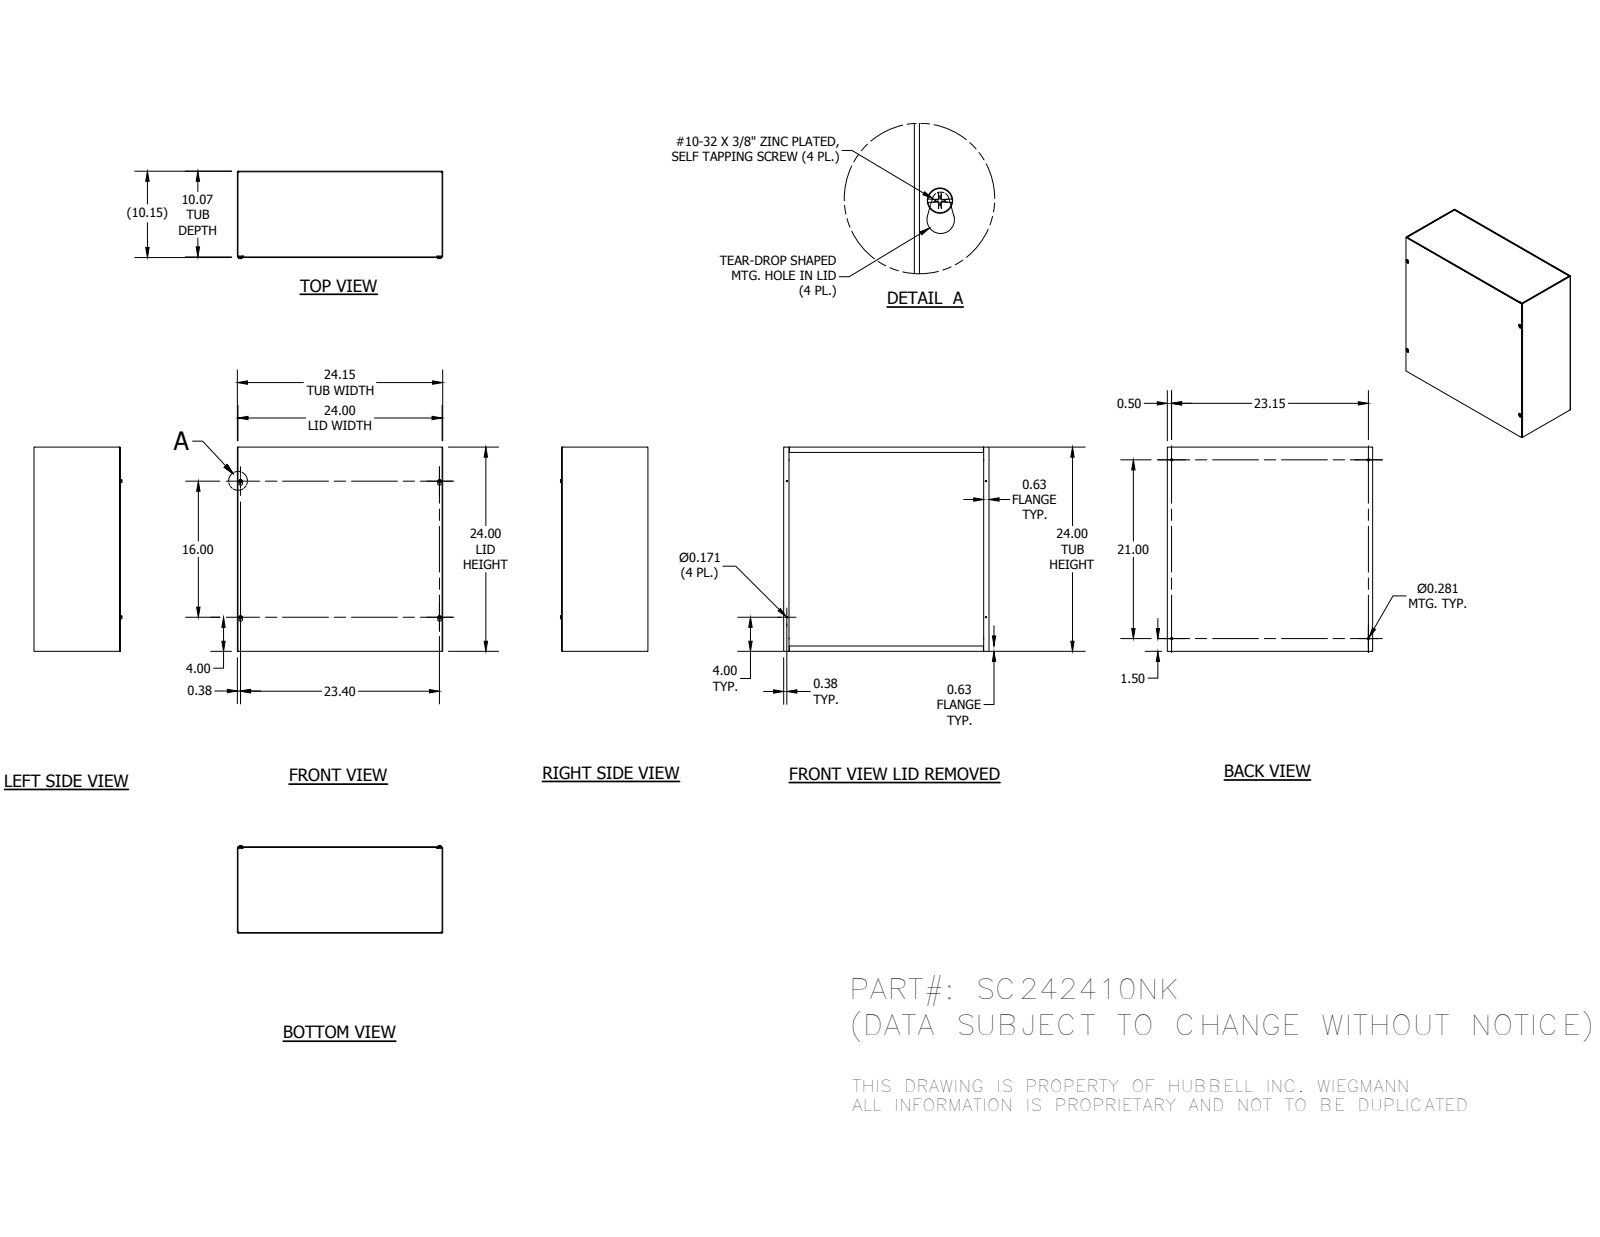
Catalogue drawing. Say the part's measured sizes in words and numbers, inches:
The part is named "SC242410NKBLR; SC2410NKTB; SC2424LPA; 37214 (+1 more)". Its 3-D file was written by "Autodesk Inventor 2014 (AUTOMOTIVE_DESIGN)". It is 8 solids with 320 faces: 192 planar, 44 cylindrical and 84 other. Overall it measures 24.148 by 24 by 10.28 inches. Its volume is 163.5 cubic inches and its surface area 4 449 square inches. Round holes: 4 of diameter 0.171, 4 of diameter 0.281. Round bosses or shafts: 4 of diameter 0.19. Partial cylindrical surfaces (rounded edges, fillets, slot ends): 12 of radius 0.016, 12 of radius 0.09, 4 of radius 0.125, 4 of radius 0.203. The main face-to-face distances are 0.074, 10.074, 10, 10.148, 24, 23.926, 24.074, 23.852, 24.148, 0.148. The hole center spacings are 2.503, 18.5, 23.407, 29.73, 16, 21, 23.148, 23.398.
